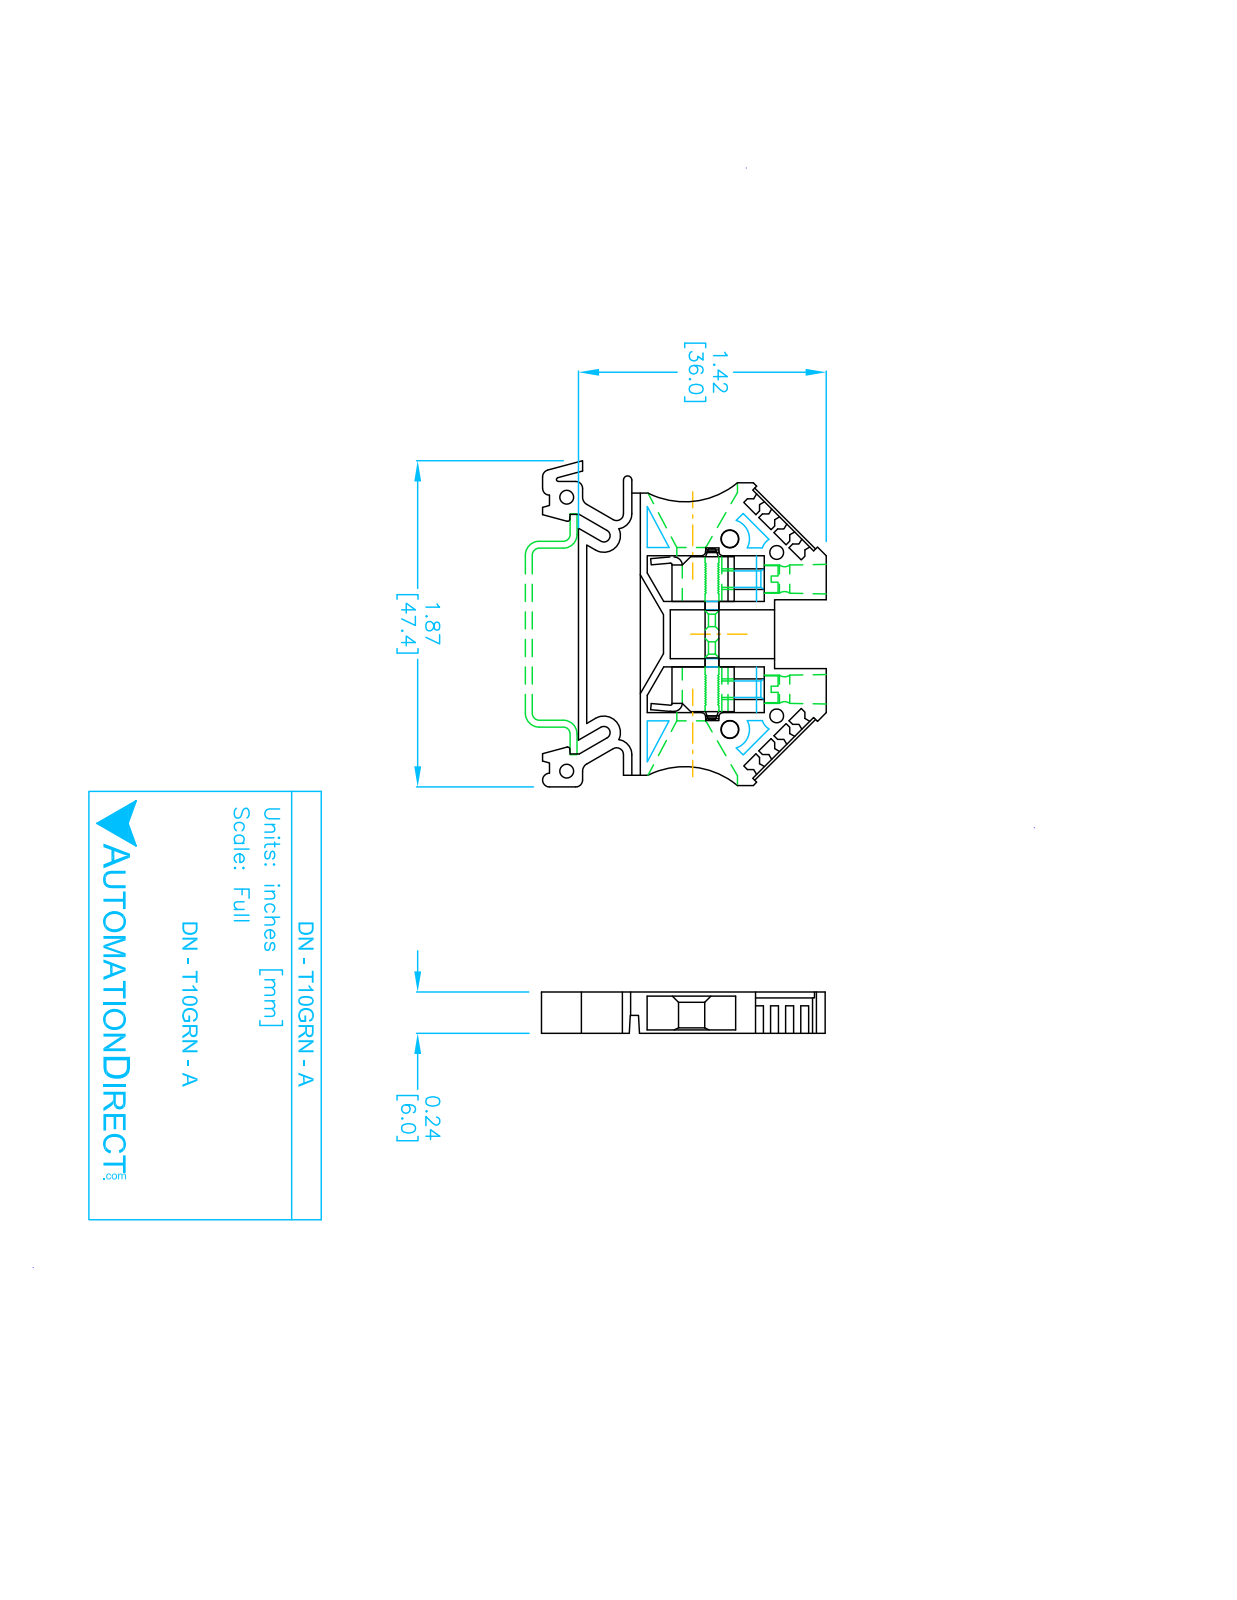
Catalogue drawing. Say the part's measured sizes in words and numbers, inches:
The part is named "DN-T10GRN-A". Its 3-D file was written by "SolidWorks 2017 (AUTOMOTIVE_DESIGN)". It is 1 solid with 181 faces: 141 planar, 40 cylindrical and 0 other. Overall it measures 1.866 by 1.622 by 0.236 inches. Its volume is 0.381 cubic inches and its surface area 7.683 square inches. Round holes: 2 of diameter 0.079, 2 of diameter 0.172. Partial cylindrical surfaces (rounded edges, fillets, slot ends): 7 of radius 0.039, 2 of radius 0.012, 2 of radius 0.035, 2 of radius 0.047, 2 of radius 0.087, 2 of radius 0.094, 2 of radius 0.472, 1 of radius 0.011. The main face-to-face distances are 0.228, 0.236, 0.142, 0.094, 0.047, 0.087, 0.134, 0.354, 0.071, 0.307. The hole center spacings are 0.63, 1.567.
